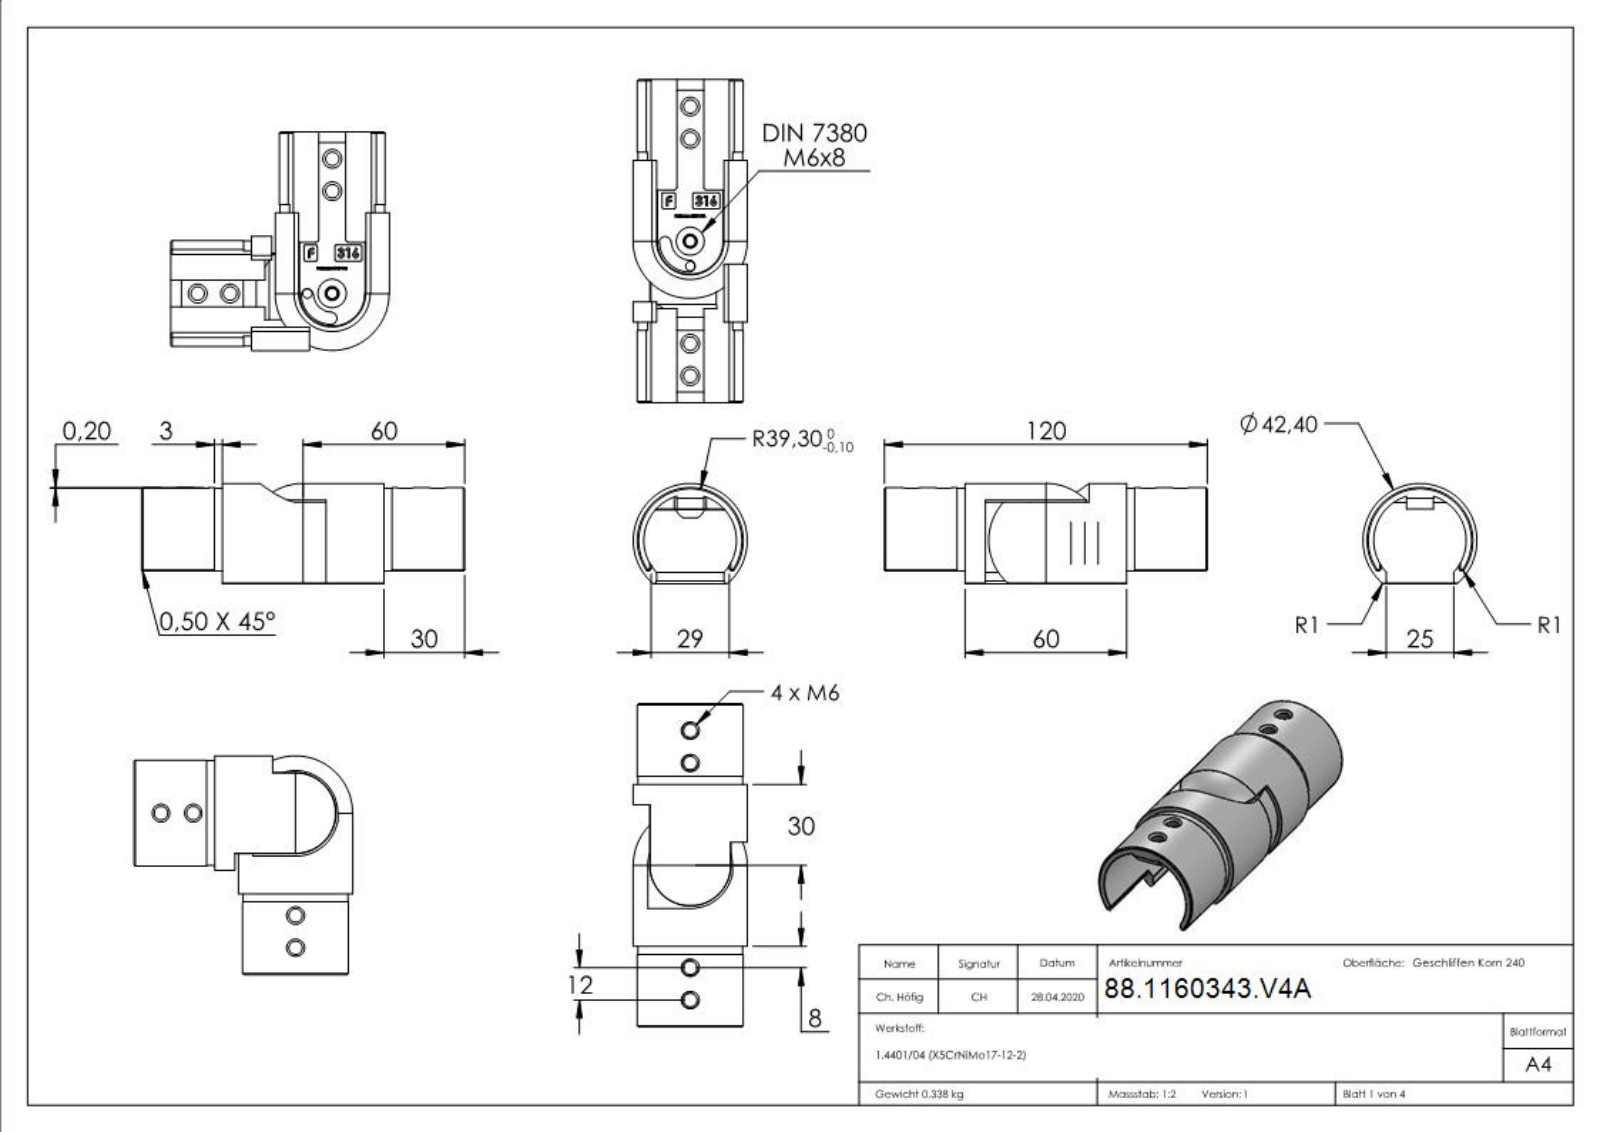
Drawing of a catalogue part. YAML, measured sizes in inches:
part_name: "60343-V4A Teil1; DIN 7380; 60343-V4A Teil2; 60343-V4A Teil2_60343-V4A Teil2 (+3 more)"
step_written_by: "SolidWorks 2015 (CONFIG_CONTROL_DESIGN)"
units: inches
bodies: {solids: 3, faces: 427, planar: 219, cylindrical: 50, other: 158}
overall_size: [4.724, 1.669, 1.485]
volume: 2.599
surface_area: 41.86
round_holes:
  - {diameter: 0.197, count: 5}
  - {diameter: 0.354, count: 1}
round_bosses_or_shafts:
  - {diameter: 0.413, count: 1}
  - {diameter: 0.315, count: 1}
  - {diameter: 0.236, count: 1}
  - {diameter: 0.138, count: 1}
partial_cylinders:
  - {radius: 0.02, count: 10}
  - {radius: 0.039, count: 8}
  - {radius: 0.089, count: 2}
  - {radius: 0.394, count: 2}
  - {radius: 0.276, count: 1}
  - {radius: 0.453, count: 1}
  - {radius: 0.492, count: 1}
  - {radius: 0.63, count: 1}
face_to_face_distances: [0.098, 0.295, 0.394, 1.181, 3.543, 0.689, 2.362, 1.063, 4.724, 0.079]
hole_center_spacings: [0.472, 1.496, 1.969, 3.465, 2.992, 3.937]
